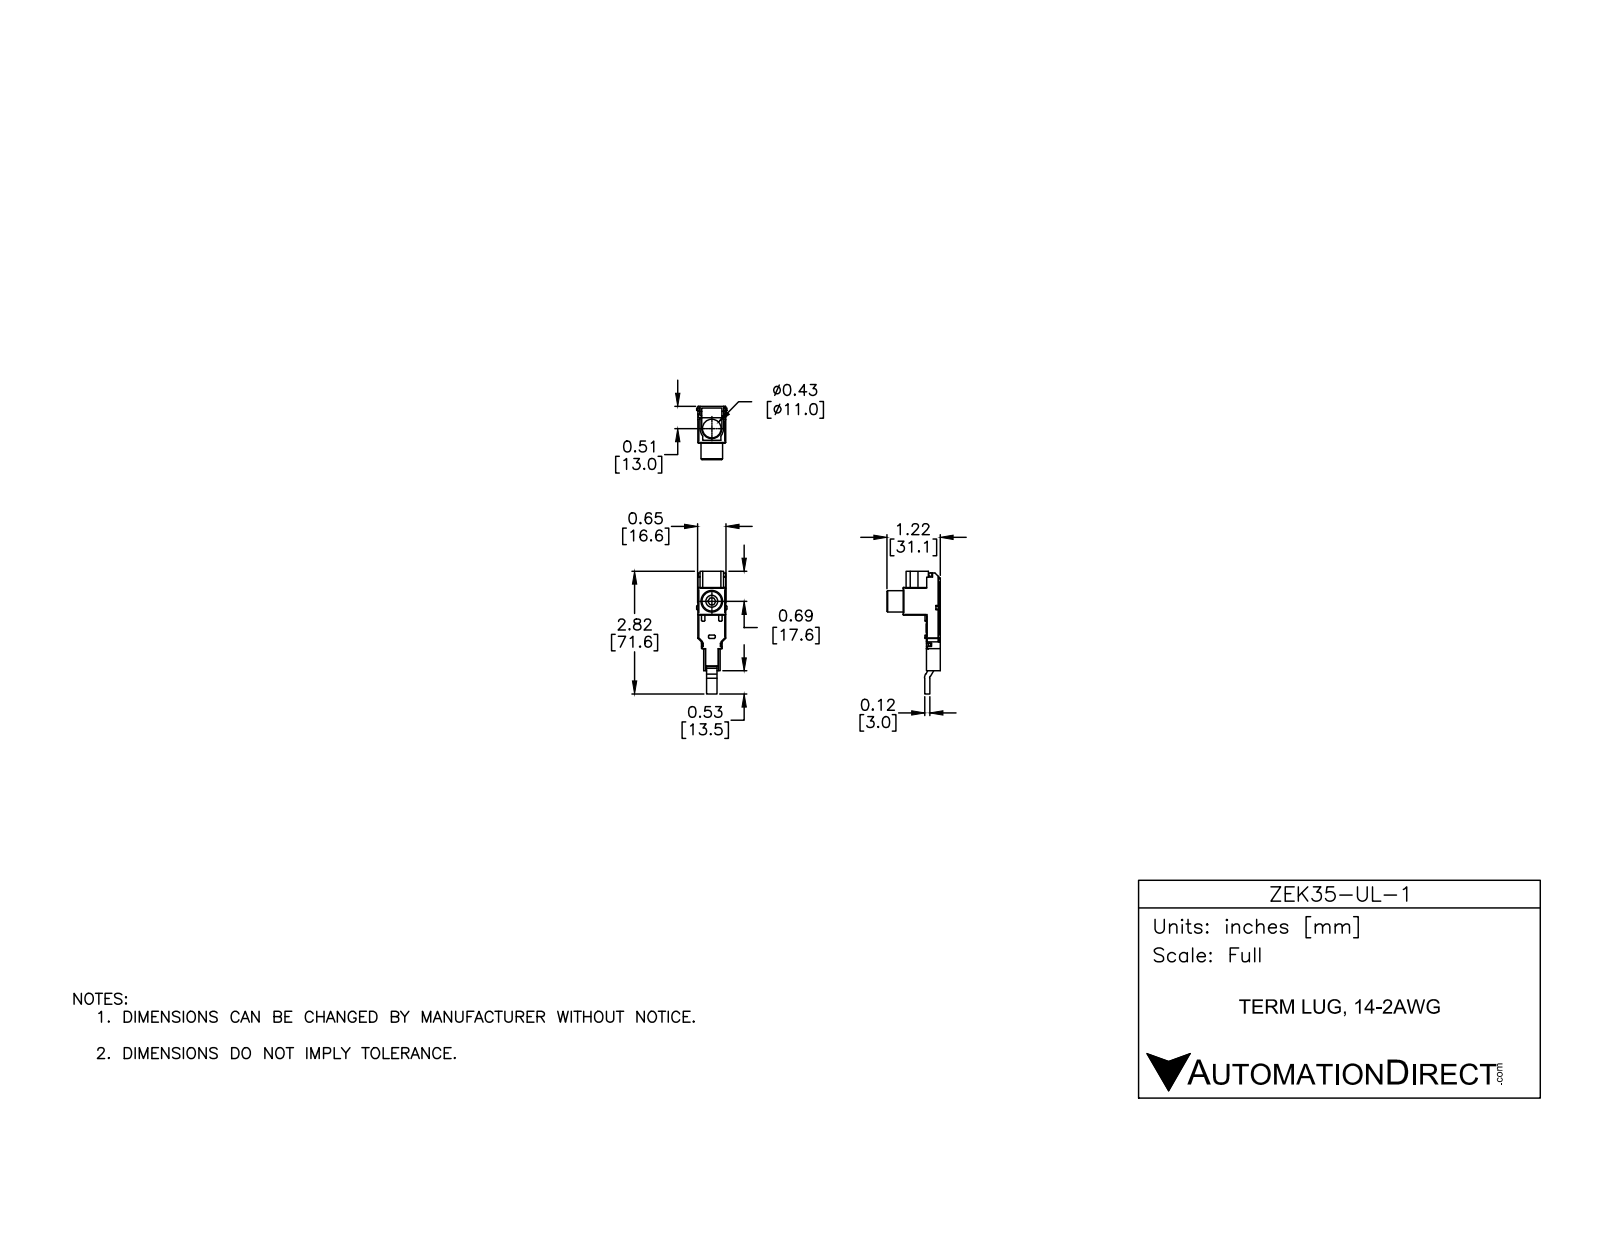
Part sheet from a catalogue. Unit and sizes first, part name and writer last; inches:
Units: inches
Overall size (bounding box): 2.819 × 1.224 × 0.693
Round holes (diameter × count): ⌀0.276 ×1, ⌀0.351 ×1, ⌀0.433 ×1
Round bosses / shafts (diameter × count): ⌀0.492 ×1, ⌀0.087 ×1
Partial cylindrical surfaces — rounded edges, fillets, slot ends (radius × count): R0.02 ×20, R0.012 ×4, R0.069 ×2, R0.079 ×2, R0.098 ×2, R0.197 ×2, R0.232 ×1, R0.272 ×1
Main face-to-face distances: 0.039, 0.043, 0.551, 0.555, 0.598, 0.047, 0.638, 0.508, 0.087, 0.594
Volume: 0.569 in³ · Surface area: 10.77 in²
Bodies: 1 solid, 222 faces (153 planar, 51 cylindrical, 18 other)
Part name (STEP PRODUCT): ZEK35-UL-1
STEP written by: SolidWorks 2023 (CONFIG_CONTROL_DESIGN)
